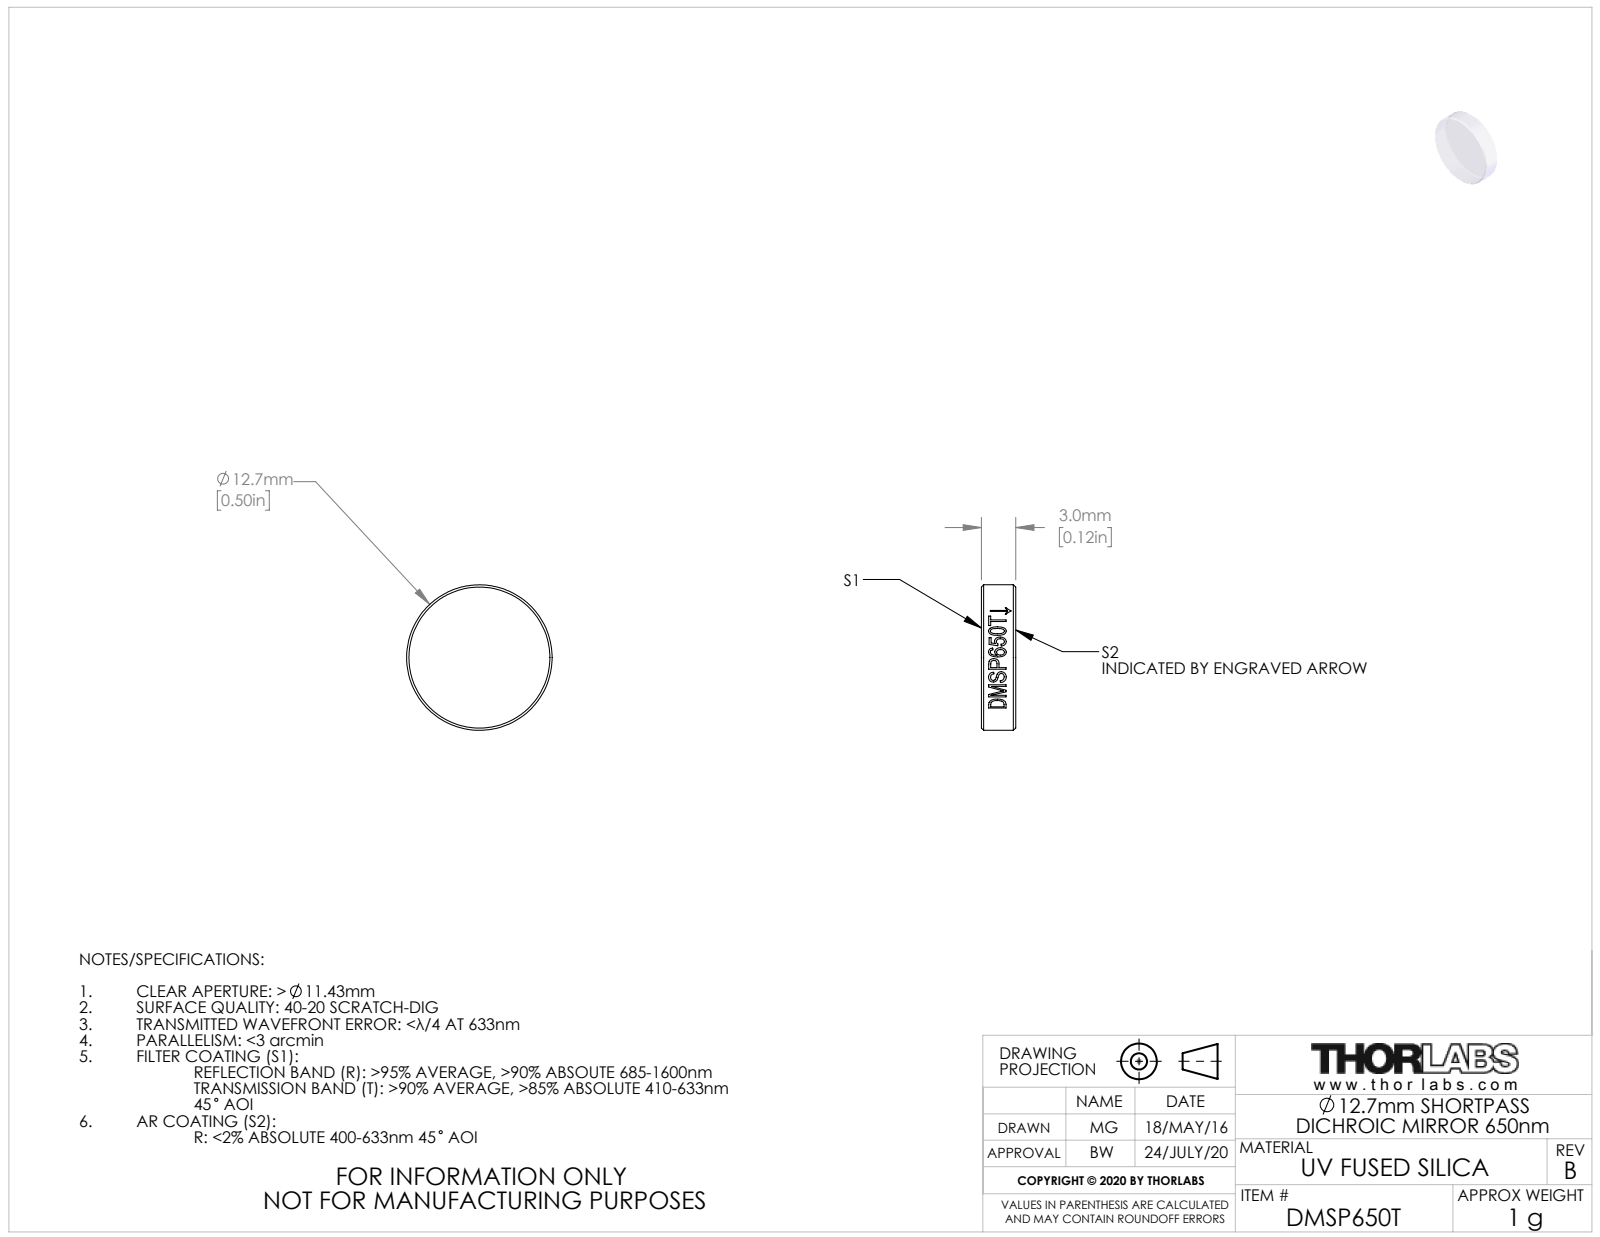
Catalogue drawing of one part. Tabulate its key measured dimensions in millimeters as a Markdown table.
| quantity | value |
| --- | --- |
| part name | TTN045288-E0W |
| STEP written by | SolidWorks 2018 (CONFIG_CONTROL_DESIGN) |
| units | millimeters |
| bodies | 1 solid, 21 faces (2 planar, 15 cylindrical, 4 other) |
| overall size | 12.7 × 12.7 × 3 |
| volume | 378 mm³ |
| surface area | 364 mm² |
| round bosses / shafts (diameter × count) | 12.7 × 1 |
| main face-to-face distances | 3 |
